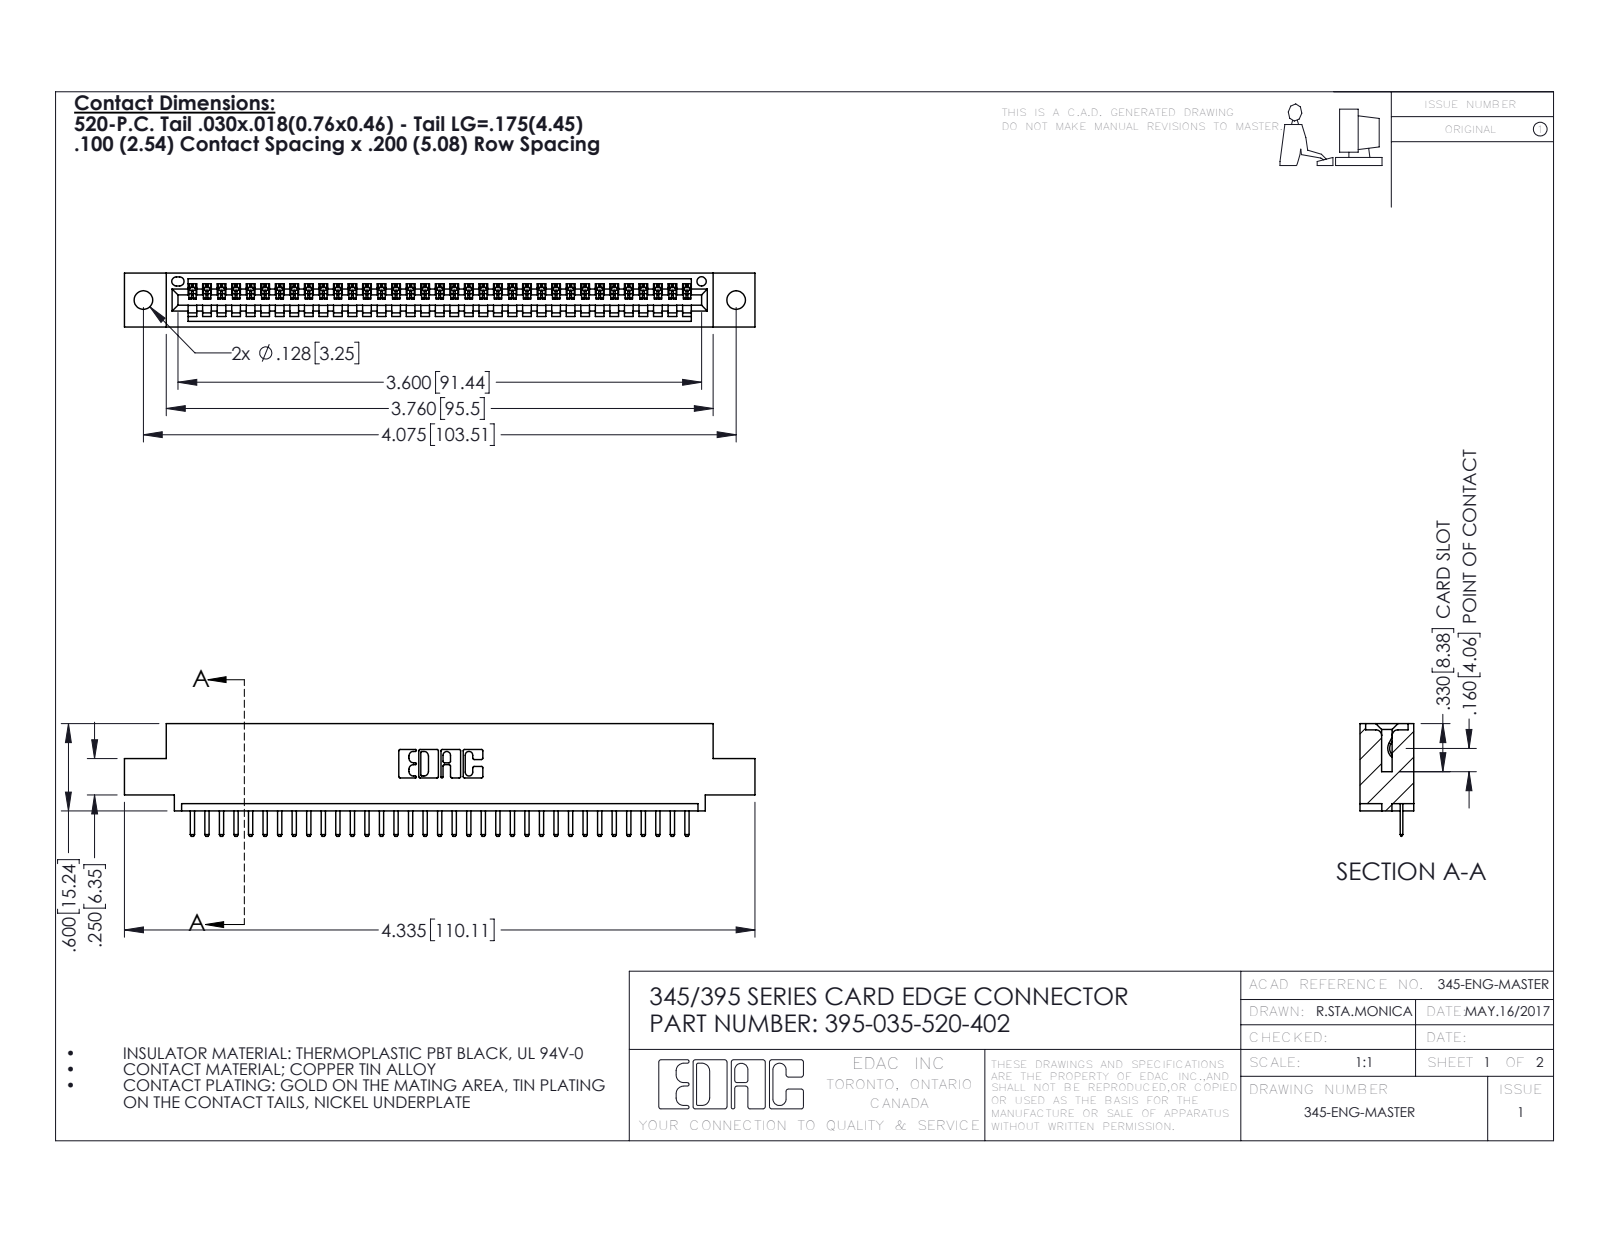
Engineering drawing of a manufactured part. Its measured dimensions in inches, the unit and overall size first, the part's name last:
Units: inches
Overall size (bounding box): 4.335 × 0.775 × 0.37
Round holes (diameter × count): ⌀0.128 ×2, ⌀0.064 ×1
Partial cylindrical surfaces — rounded edges, fillets, slot ends (radius × count): R0.01 ×72, R0.006 ×70, R0.01 ×22, R0.007 ×6, R0.031 ×6, R0.026 ×3, R0.031 ×2, R0.04 ×2
Main face-to-face distances: 0.298, 0.072, 0.37, 0.2, 0.098, 0.272, 0.025, 0.225, 0.072, 0.149
Hole centre spacings: 0.27, 3.839, 4.075
Volume: 0.622 in³ · Surface area: 20.04 in²
Bodies: 36 solids, 2300 faces (1554 planar, 746 cylindrical, 0 other)
Part name (STEP PRODUCT): 345-292-001_345-293-120; 345 Part_0.110 Offset - 0.128 Dia; 395-035-520-402
STEP written by: SolidWorks 2016 (CONFIG_CONTROL_DESIGN)
